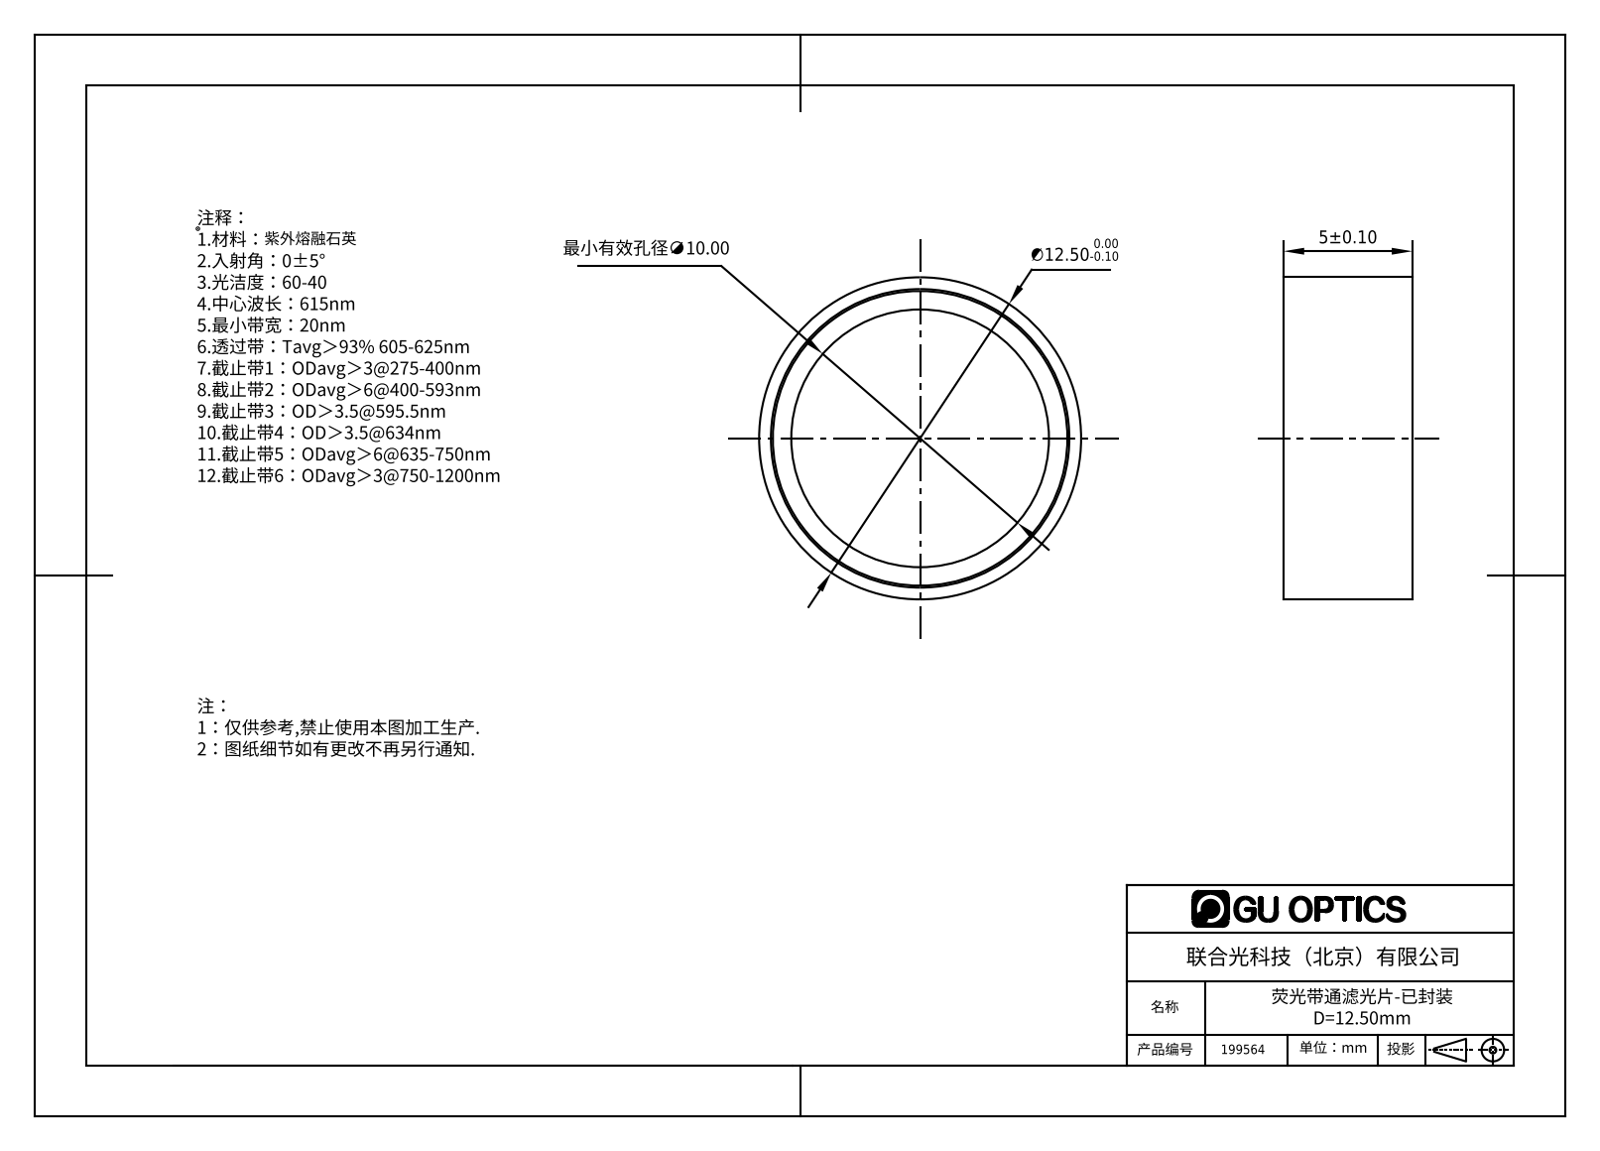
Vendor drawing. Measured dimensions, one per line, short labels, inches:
name: 199480
written by: SolidWorks 2019 (CONFIG_CONTROL_DESIGN)
unit: in
bodies: 3 solids, 22 faces (8 planar, 14 cylindrical, 0 other)
size: 0.509 × 0.509 × 0.197
volume: 0.023 in³; area: 1.36 in²
holes: 1× ⌀0.347, 1× ⌀0.409, 1× ⌀0.449, 1× ⌀0.472
bosses: 1× ⌀0.509, 1× ⌀0.45
face distances: 0.079, 0.059, 0.138, 0.153, 0.094, 0.015, 0.197, 0.044, 0.02, 0.074
